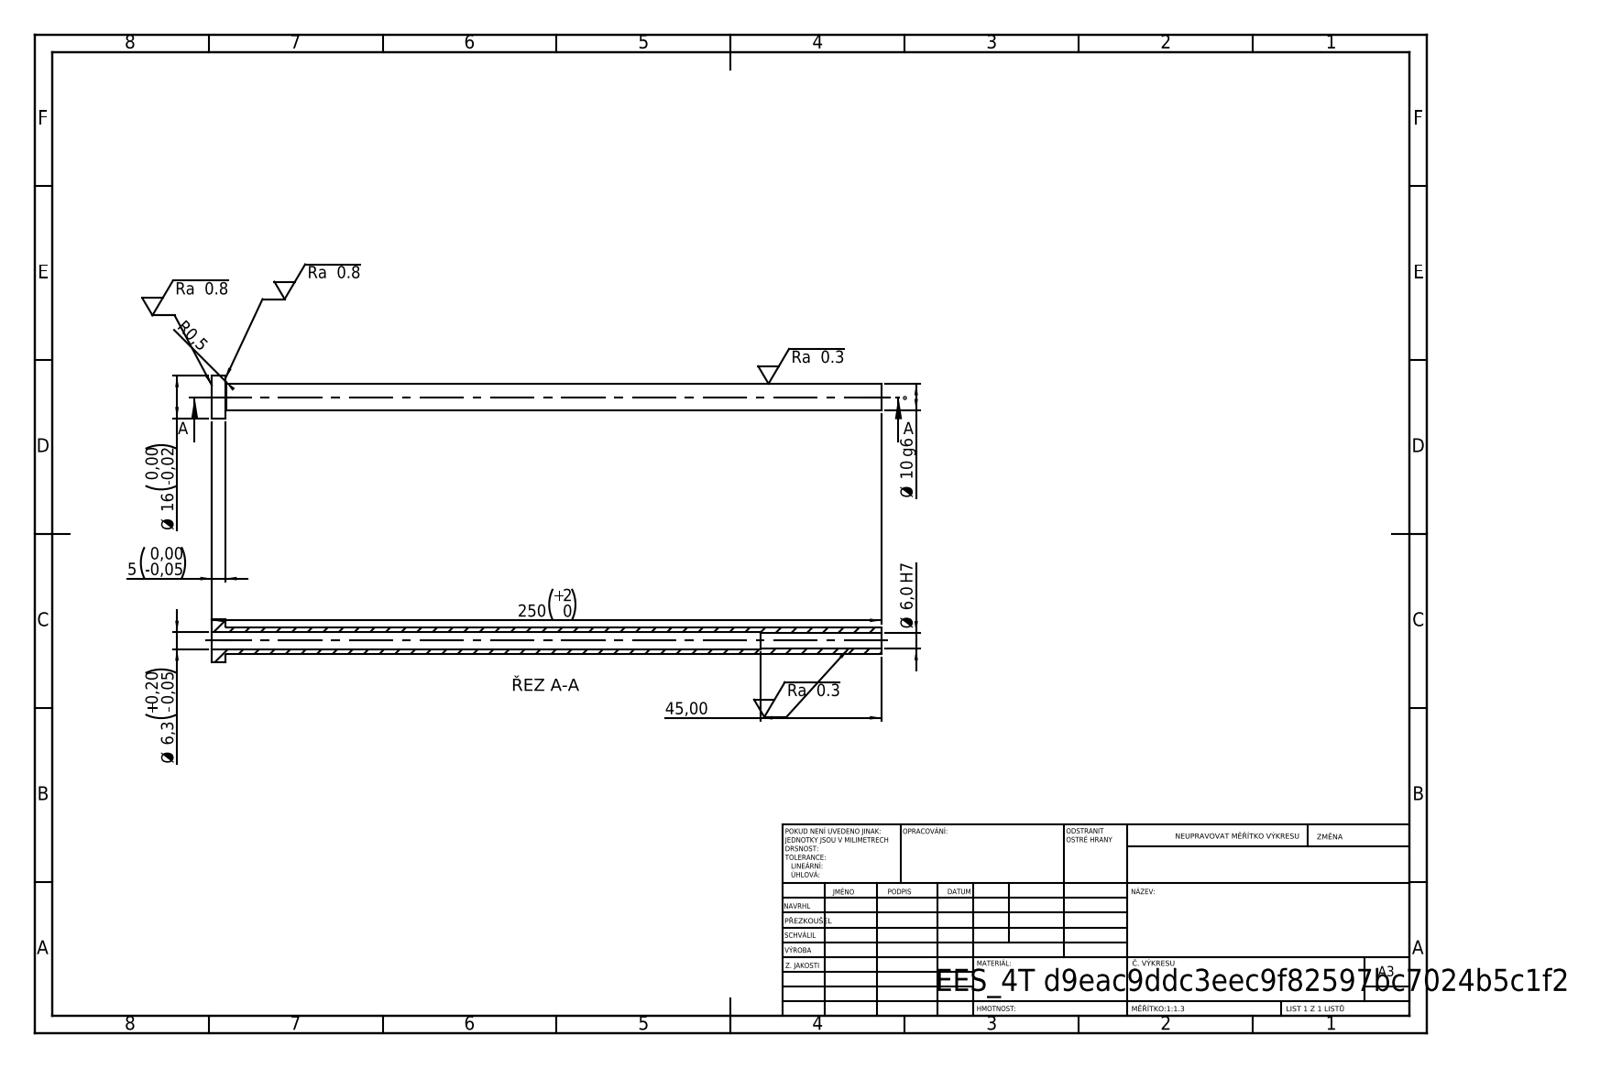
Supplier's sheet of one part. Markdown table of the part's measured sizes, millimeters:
| quantity | value |
| --- | --- |
| STEP written by | SolidWorks 2019 (CONFIG_CONTROL_DESIGN) |
| units | millimeters |
| bodies | 1 solid, 14 faces (4 planar, 8 cylindrical, 2 other) |
| overall size | 250 × 16 × 16 |
| volume | 12 587 mm³ |
| surface area | 13 193 mm² |
| round holes (diameter × count) | 6 × 1, 6.3 × 1 |
| round bosses / shafts (diameter × count) | 16 × 1, 10 × 1 |
| main face-to-face distances | 5, 250, 245, 205, 200, 45 |
